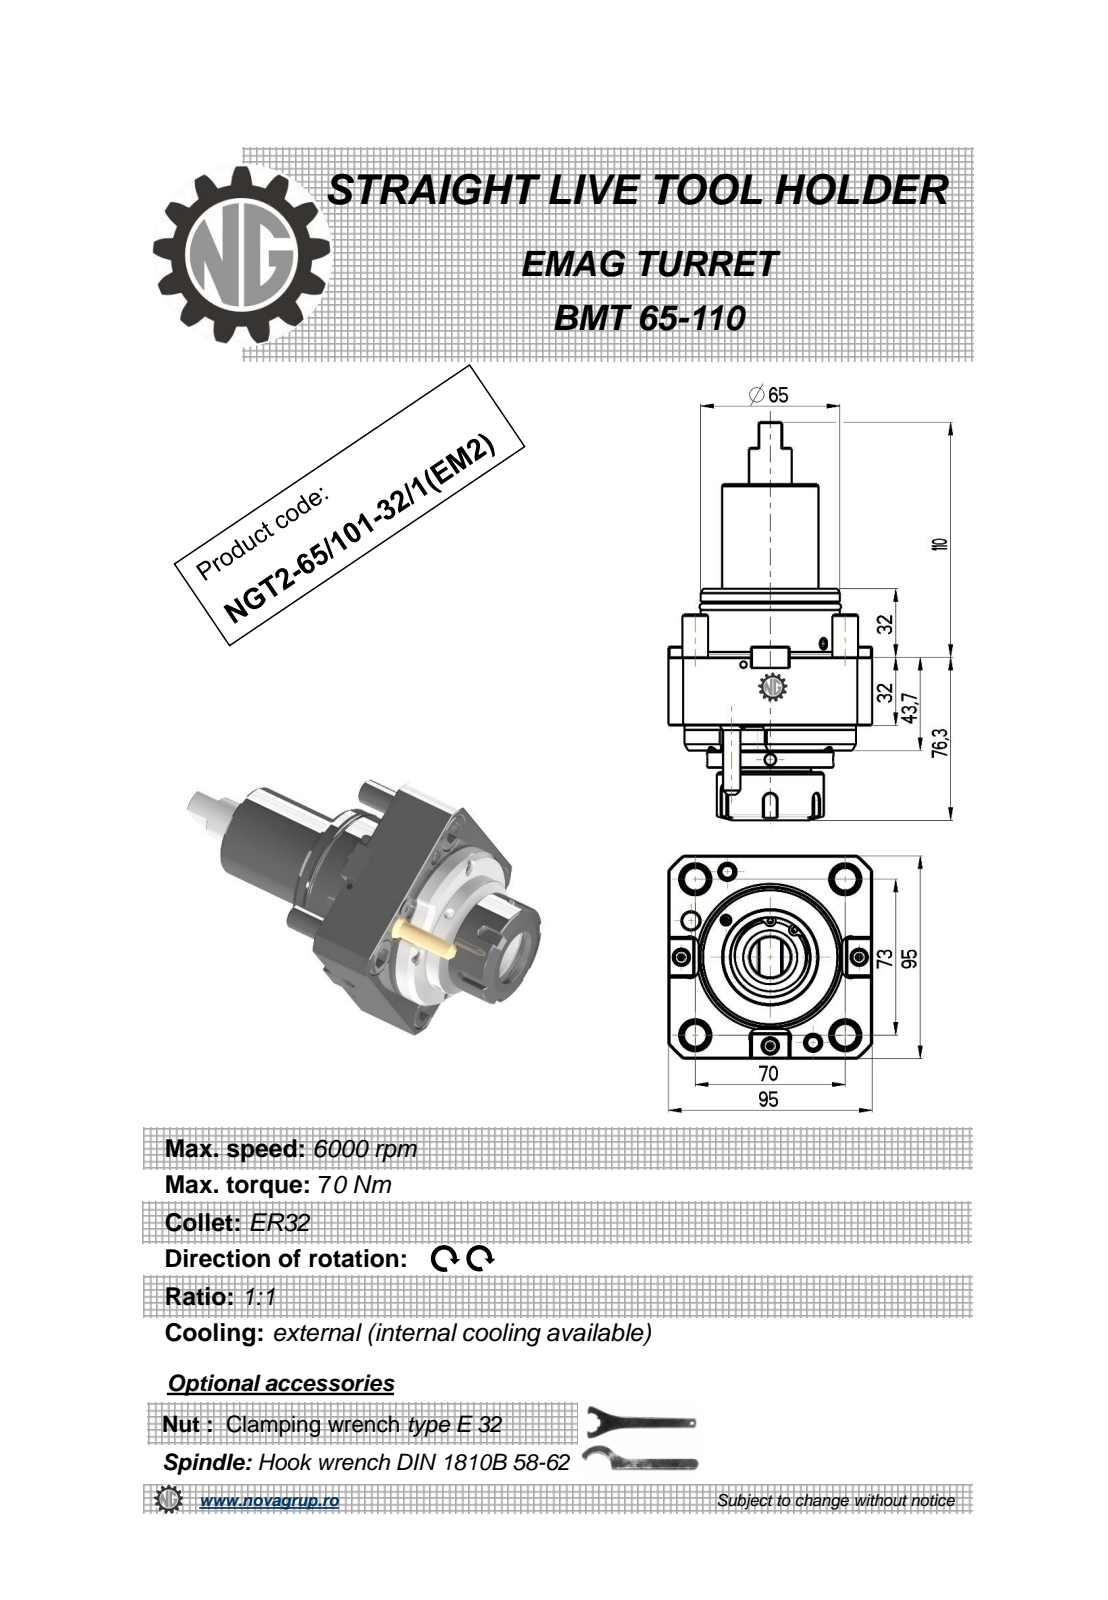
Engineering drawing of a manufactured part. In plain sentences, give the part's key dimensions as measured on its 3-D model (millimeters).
The part is named "NGT2_65_101_32_1_EM2". Its 3-D file was written by "PRO/ENGINEER BY PARAMETRIC TECHNOLOGY CORPORATION, 2010280 (CONFIG_CONTROL_DESIGN)". It is 2 solids with 269 faces: 115 planar, 66 cylindrical and 88 other. Overall it measures 186.3 by 95 by 95 millimeters. Its volume is 609 710 cubic millimeters and its surface area 64 733 square millimeters. Round holes: 3 of diameter 5, 1 of diameter 3, 1 of diameter 8, 1 of diameter 27. Round bosses or shafts: 4 of diameter 12, 1 of diameter 80, 1 of diameter 65, 1 of diameter 60, 1 of diameter 59, 1 of diameter 50, 1 of diameter 46, 1 of diameter 45. Partial cylindrical surfaces (rounded edges, fillets, slot ends): 6 of radius 0.22, 5 of radius 3, 3 of radius 6, 2 of radius 0.8, 1 of radius 62.5. The main face-to-face distances are 32, 95, 43.7, 11.7, 64, 75.7, 83.7, 51.7, 19.7, 8. The hole center spacings are 40.7, 40.72, 56.77.
